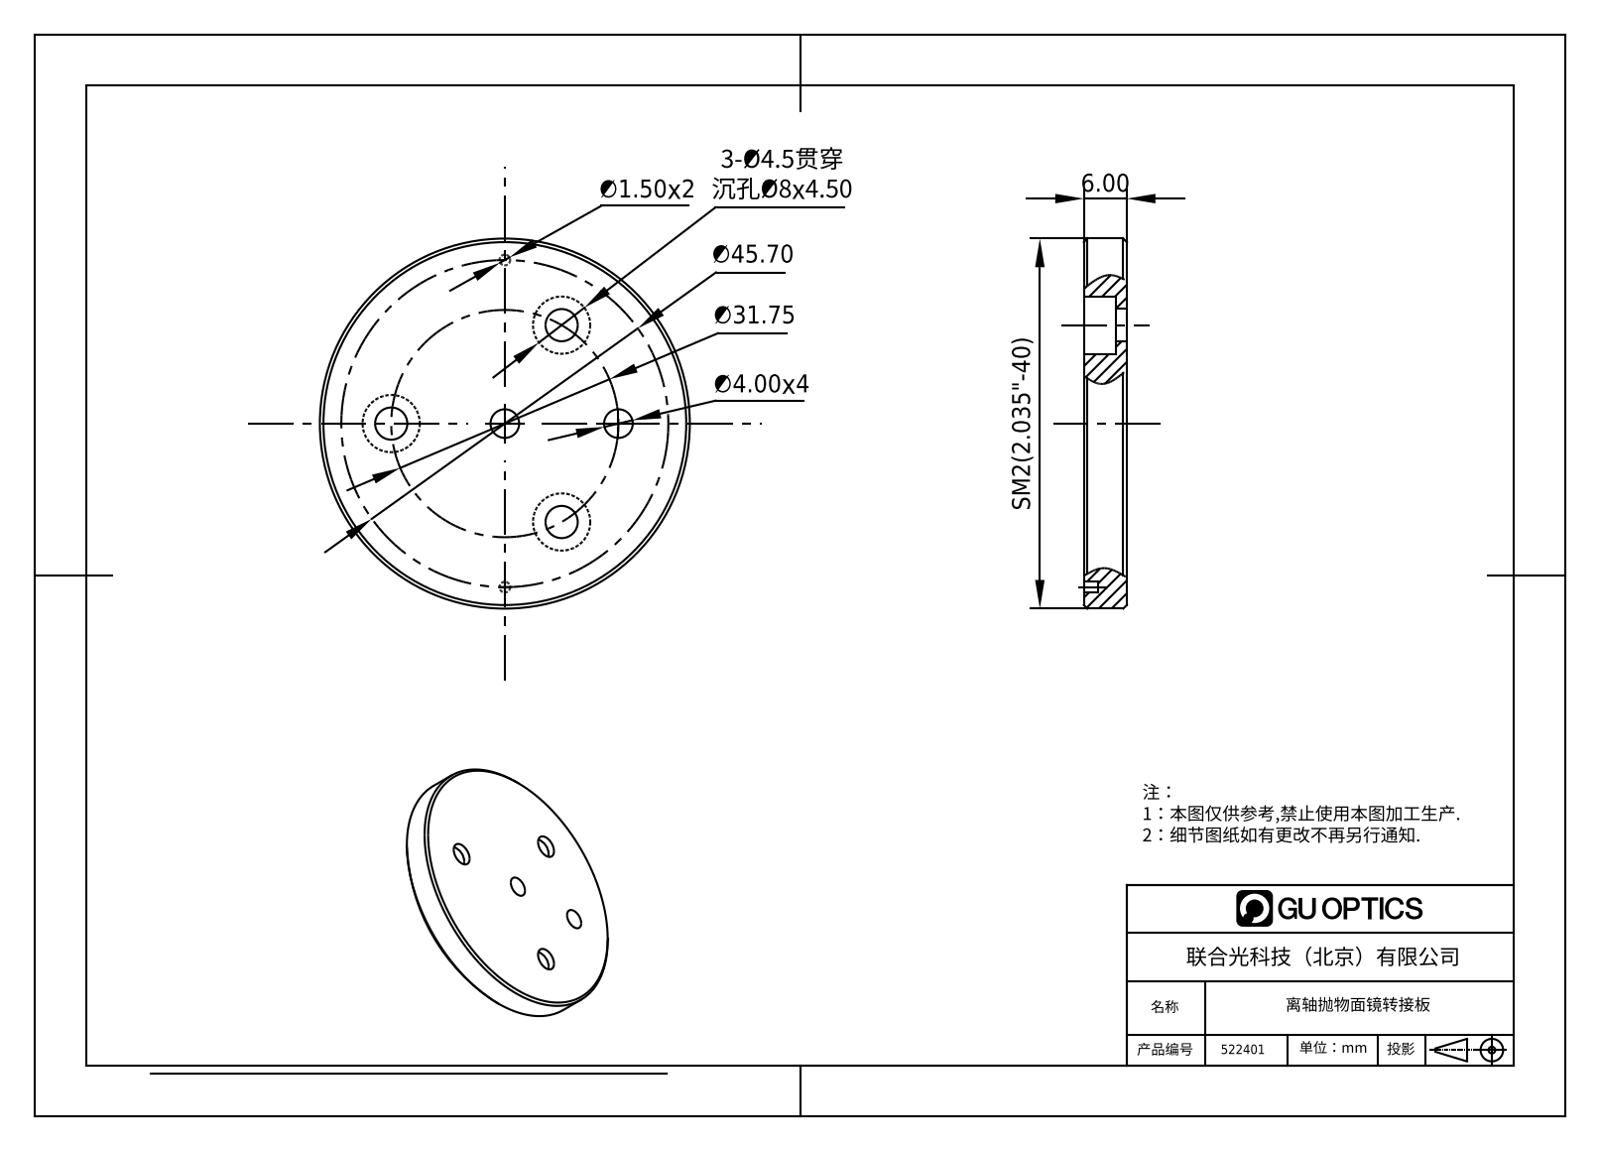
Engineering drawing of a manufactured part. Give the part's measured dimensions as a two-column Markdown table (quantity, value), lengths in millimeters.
| quantity | value |
| --- | --- |
| part name | 522401 |
| STEP written by | SolidWorks 2020 (CONFIG_CONTROL_DESIGN) |
| units | millimeters |
| bodies | 1 solid, 26 faces (10 planar, 11 cylindrical, 5 other) |
| overall size | 51.69 × 51.69 × 6 |
| volume | 11 288 mm³ |
| surface area | 6 001 mm² |
| round holes (diameter × count) | 4.5 × 3, 8 × 3, 1.5 × 2, 4 × 2 |
| round bosses / shafts (diameter × count) | 51.69 × 1 |
| main face-to-face distances | 6, 4.5, 1.5, 2, 2.5, 4 |
| hole center spacings | 15.88, 27.83, 27.5, 12.08, 22.85, 37.45, 31.76, 45.7 |
